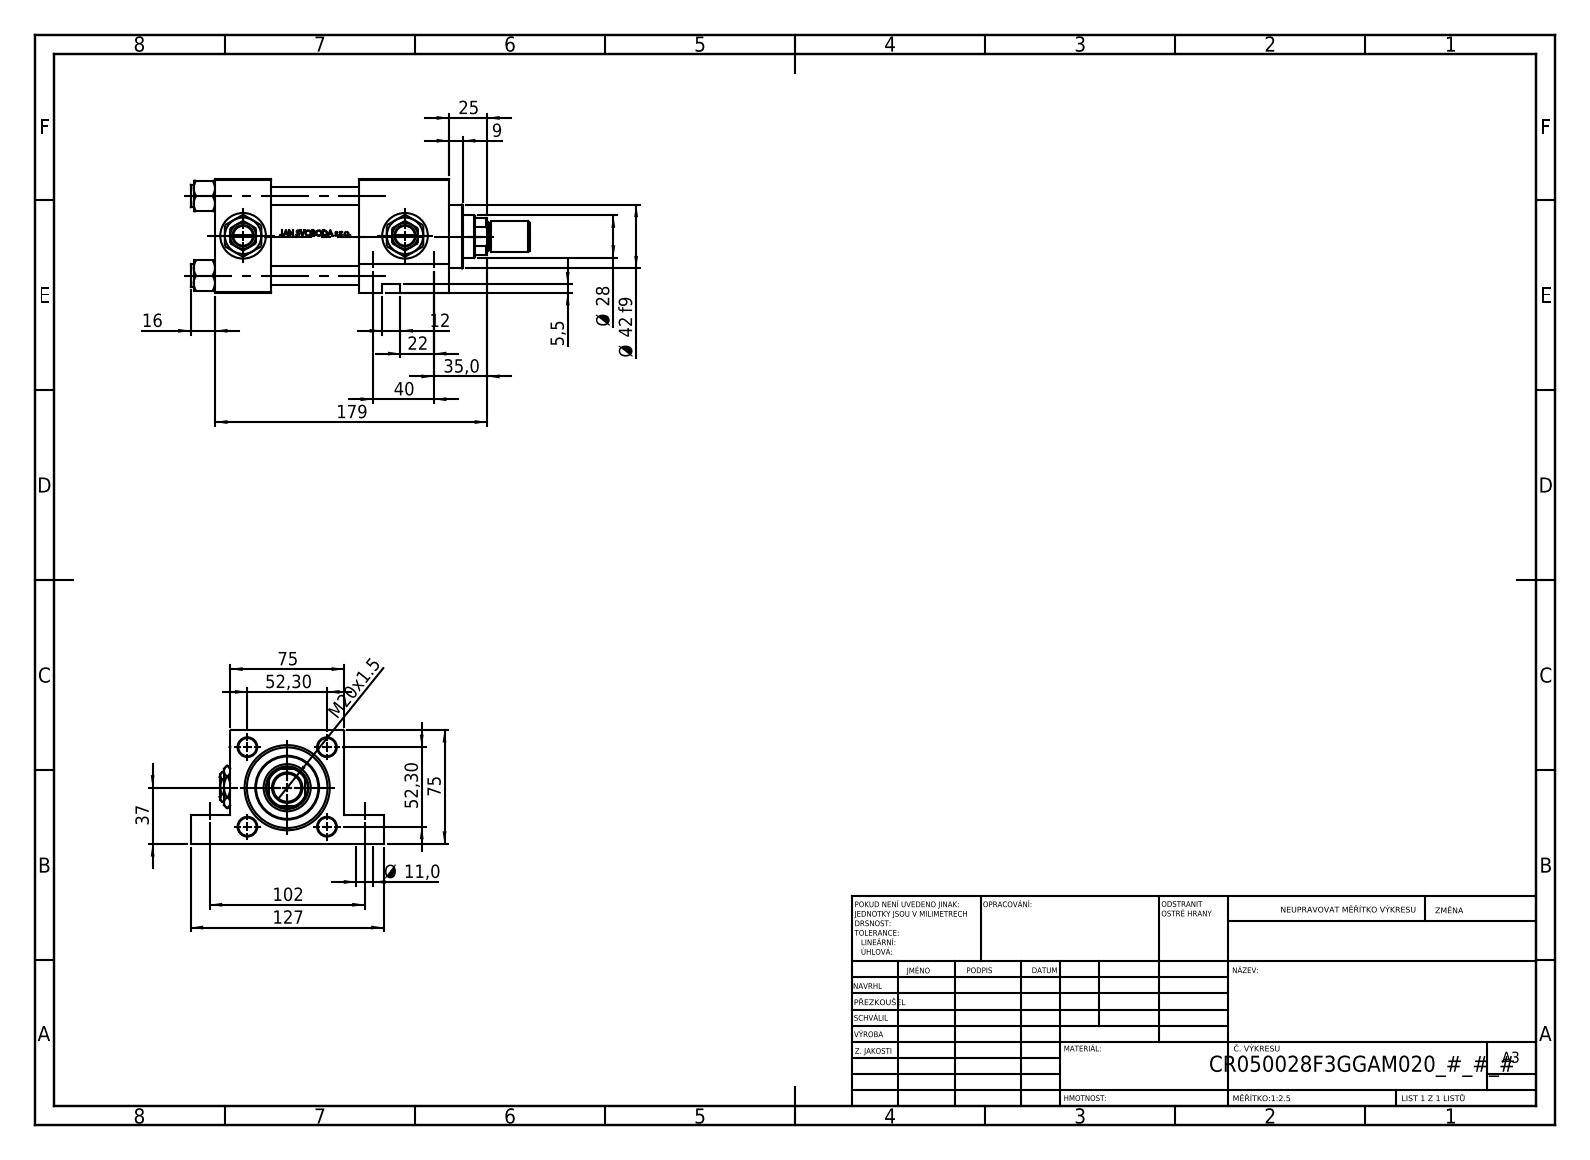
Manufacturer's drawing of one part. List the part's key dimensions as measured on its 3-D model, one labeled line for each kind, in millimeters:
Part name (STEP PRODUCT): V215_VC_A; Zatka_pro_OIL_PORT; V215CR_VCP_F; NUT_M5_F (+3 more)
STEP written by: SolidWorks 2019 (CONFIG_CONTROL_DESIGN)
Units: millimetres
Bodies: 14 solids, 1216 faces (488 planar, 140 cylindrical, 588 other)
Overall size (bounding box): 223 × 127 × 75
Volume: 721 579 mm³ · Surface area: 166 849 mm²
Round holes (diameter × count): ⌀12 ×4, ⌀20.96 ×4, ⌀30 ×4, ⌀7 ×3, ⌀11 ×2, ⌀11 ×2, ⌀18.5 ×1, ⌀28 ×1, ⌀31 ×1, ⌀41 ×1, ⌀50 ×1, ⌀53 ×1
Round bosses / shafts (diameter × count): ⌀15 ×4, ⌀56 ×1, ⌀42 ×1, ⌀20 ×1, ⌀18 ×1
Partial cylindrical surfaces — rounded edges, fillets, slot ends (radius × count): R13.5 ×1
Main face-to-face distances: 75, 37, 154, 117, 58, 95, 59, 19, 56, 74.8
Hole centre spacings: 52.3, 36.63, 37.34, 40, 51.62, 60.21, 73.96, 99.56
